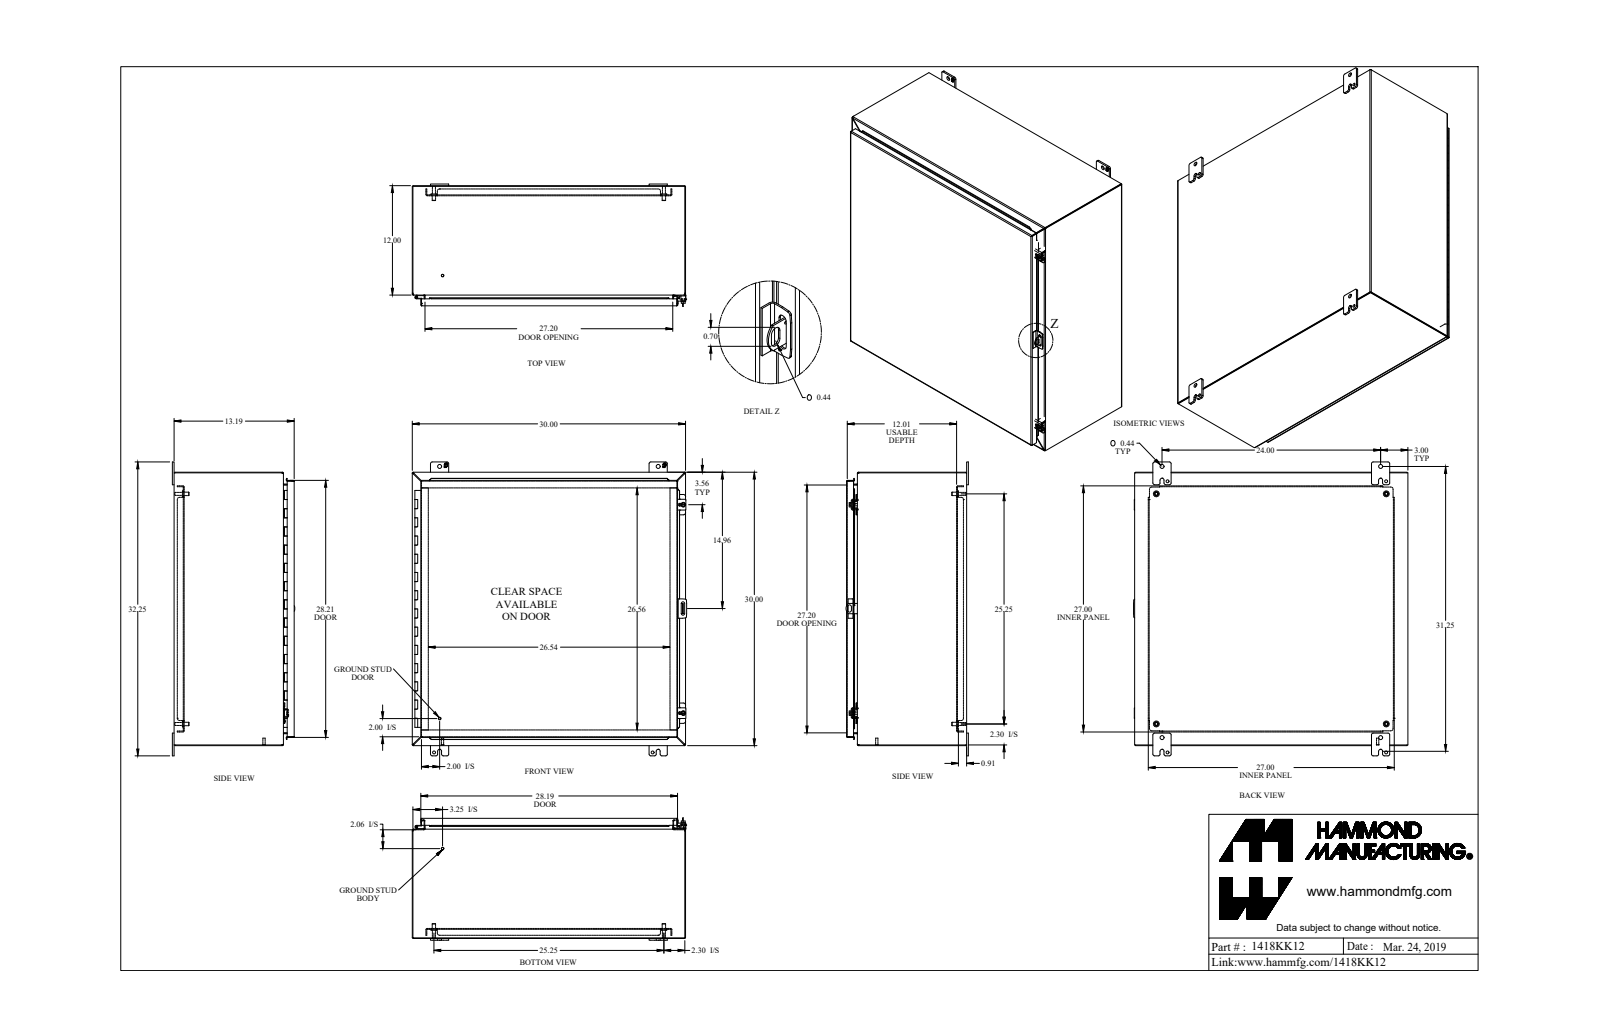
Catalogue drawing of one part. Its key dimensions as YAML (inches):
part_name: "1418KK12_Default"
step_written_by: "SolidWorks 2019 (CONFIG_CONTROL_DESIGN)"
units: inches
bodies: {solids: 43, faces: 1305, planar: 785, cylindrical: 444, other: 76}
overall_size: [32.25, 30.125, 13.437]
volume: 366.8
surface_area: 9577
round_holes:
  - {diameter: 0.313, count: 4}
  - {diameter: 0.437, count: 4}
  - {diameter: 0.5, count: 4}
  - {diameter: 0.213, count: 2}
  - {diameter: 0.265, count: 2}
  - {diameter: 0.307, count: 2}
  - {diameter: 0.375, count: 2}
  - {diameter: 0.445, count: 2}
  - {diameter: 0.125, count: 1}
  - {diameter: 0.187, count: 1}
round_bosses_or_shafts:
  - {diameter: 0.65, count: 4}
  - {diameter: 0.375, count: 4}
  - {diameter: 0.33, count: 4}
  - {diameter: 1, count: 2}
  - {diameter: 0.5, count: 2}
  - {diameter: 0.39, count: 2}
  - {diameter: 0.281, count: 2}
  - {diameter: 0.25, count: 2}
partial_cylinders:
  - {radius: 0.188, count: 34}
  - {radius: 0.036, count: 22}
  - {radius: 0.108, count: 22}
  - {radius: 0.25, count: 20}
  - {radius: 0.048, count: 13}
  - {radius: 0.143, count: 13}
  - {radius: 0.116, count: 12}
  - {radius: 0.04, count: 8}
face_to_face_distances: [0.072, 13.113, 29.928, 13.041, 13.185, 0.095, 0.937, 1.009, 12.081, 12.009]
hole_center_spacings: [25.25, 1.736, 24, 29.75, 35.709, 38.224, 25.25, 1.625]
